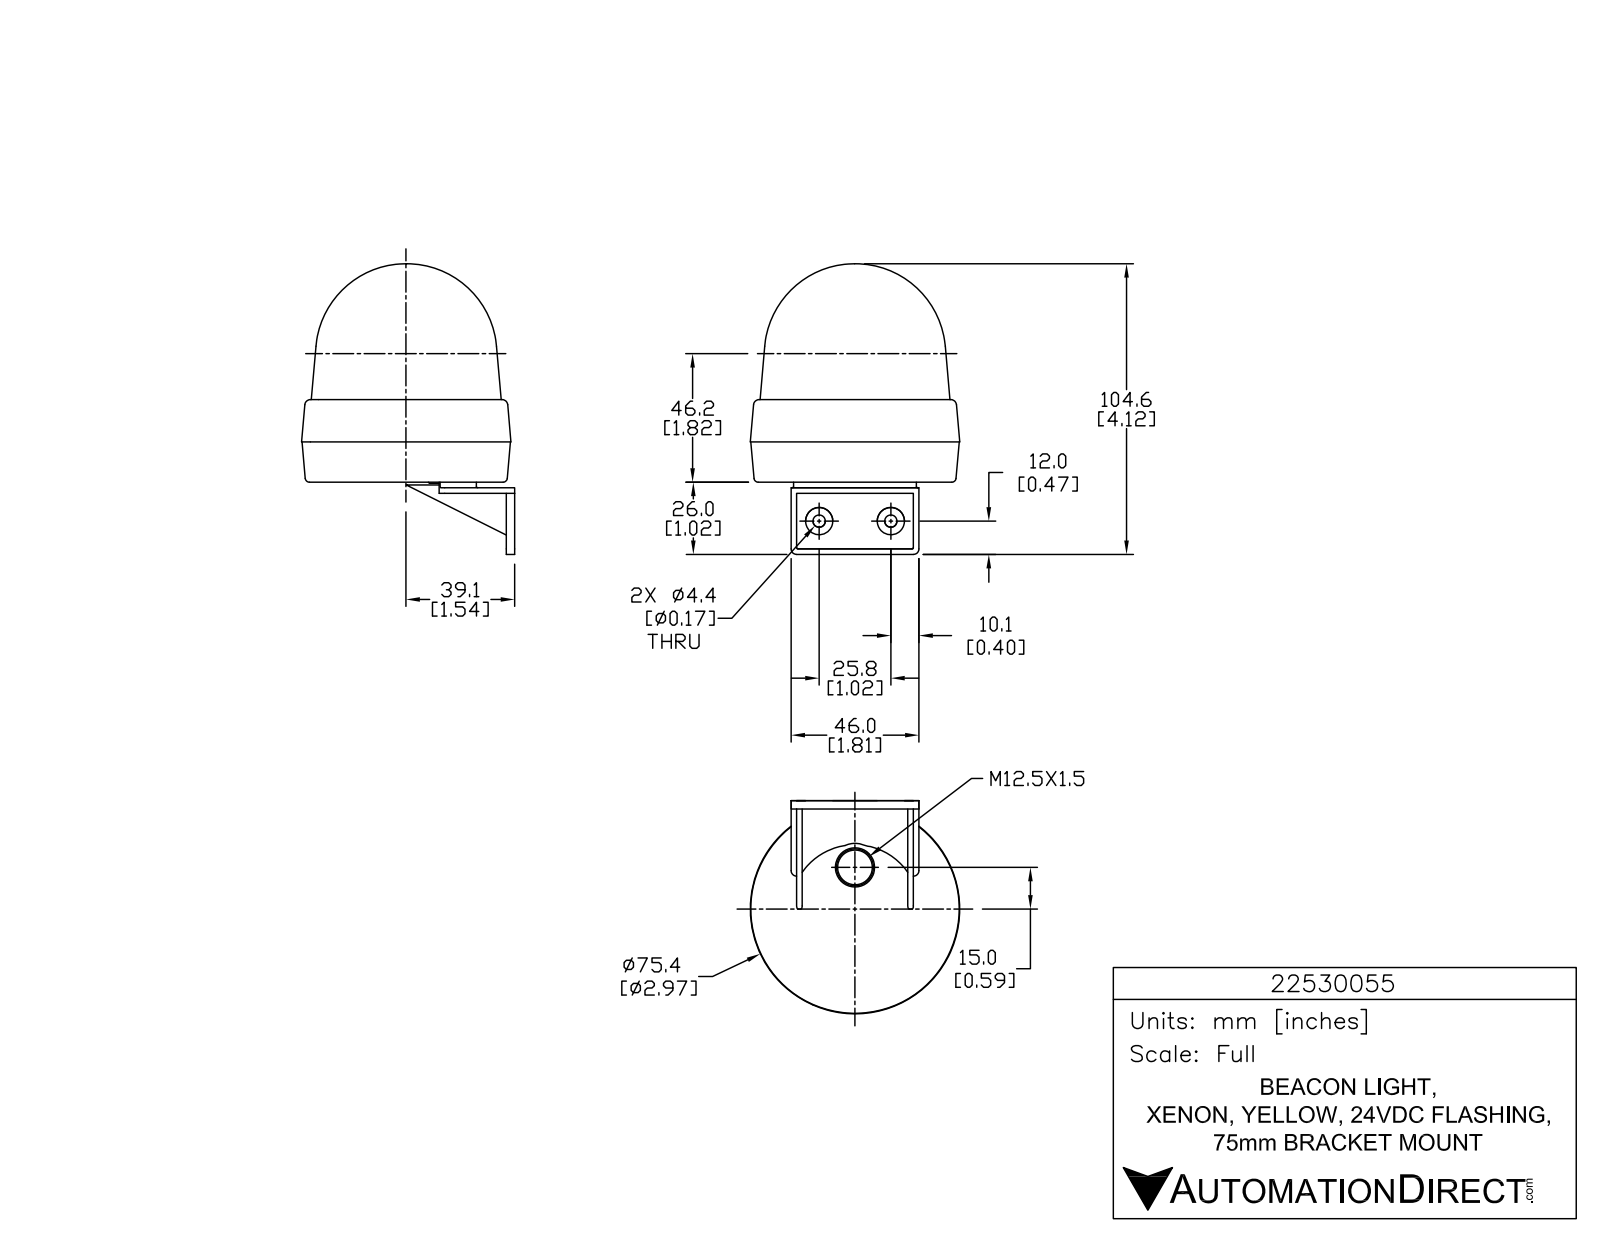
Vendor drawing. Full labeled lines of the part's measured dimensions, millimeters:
Part name (STEP PRODUCT): 22530055
STEP written by: SolidWorks 2015 (AUTOMOTIVE_DESIGN)
Units: millimetres
Bodies: 1 solid, 819 faces (549 planar, 180 cylindrical, 90 other)
Overall size (bounding box): 104.6 × 82.6 × 75.4
Volume: 262 500 mm³ · Surface area: 27 080 mm²
Round holes (diameter × count): ⌀1.5 ×3, ⌀4.4 ×2
Round bosses / shafts (diameter × count): ⌀8.6 ×3, ⌀2.1 ×3, ⌀9.8 ×2
Partial cylindrical surfaces — rounded edges, fillets, slot ends (radius × count): R0.1 ×9, R0.1 ×6, R0.3 ×6, R0.3 ×6, R0.3 ×6, R0.5 ×6, R5 ×6, R2 ×4
Main face-to-face distances: 2, 4, 40, 1, 3, 42, 38, 2, 42, 44
Hole centre spacings: 25.8
